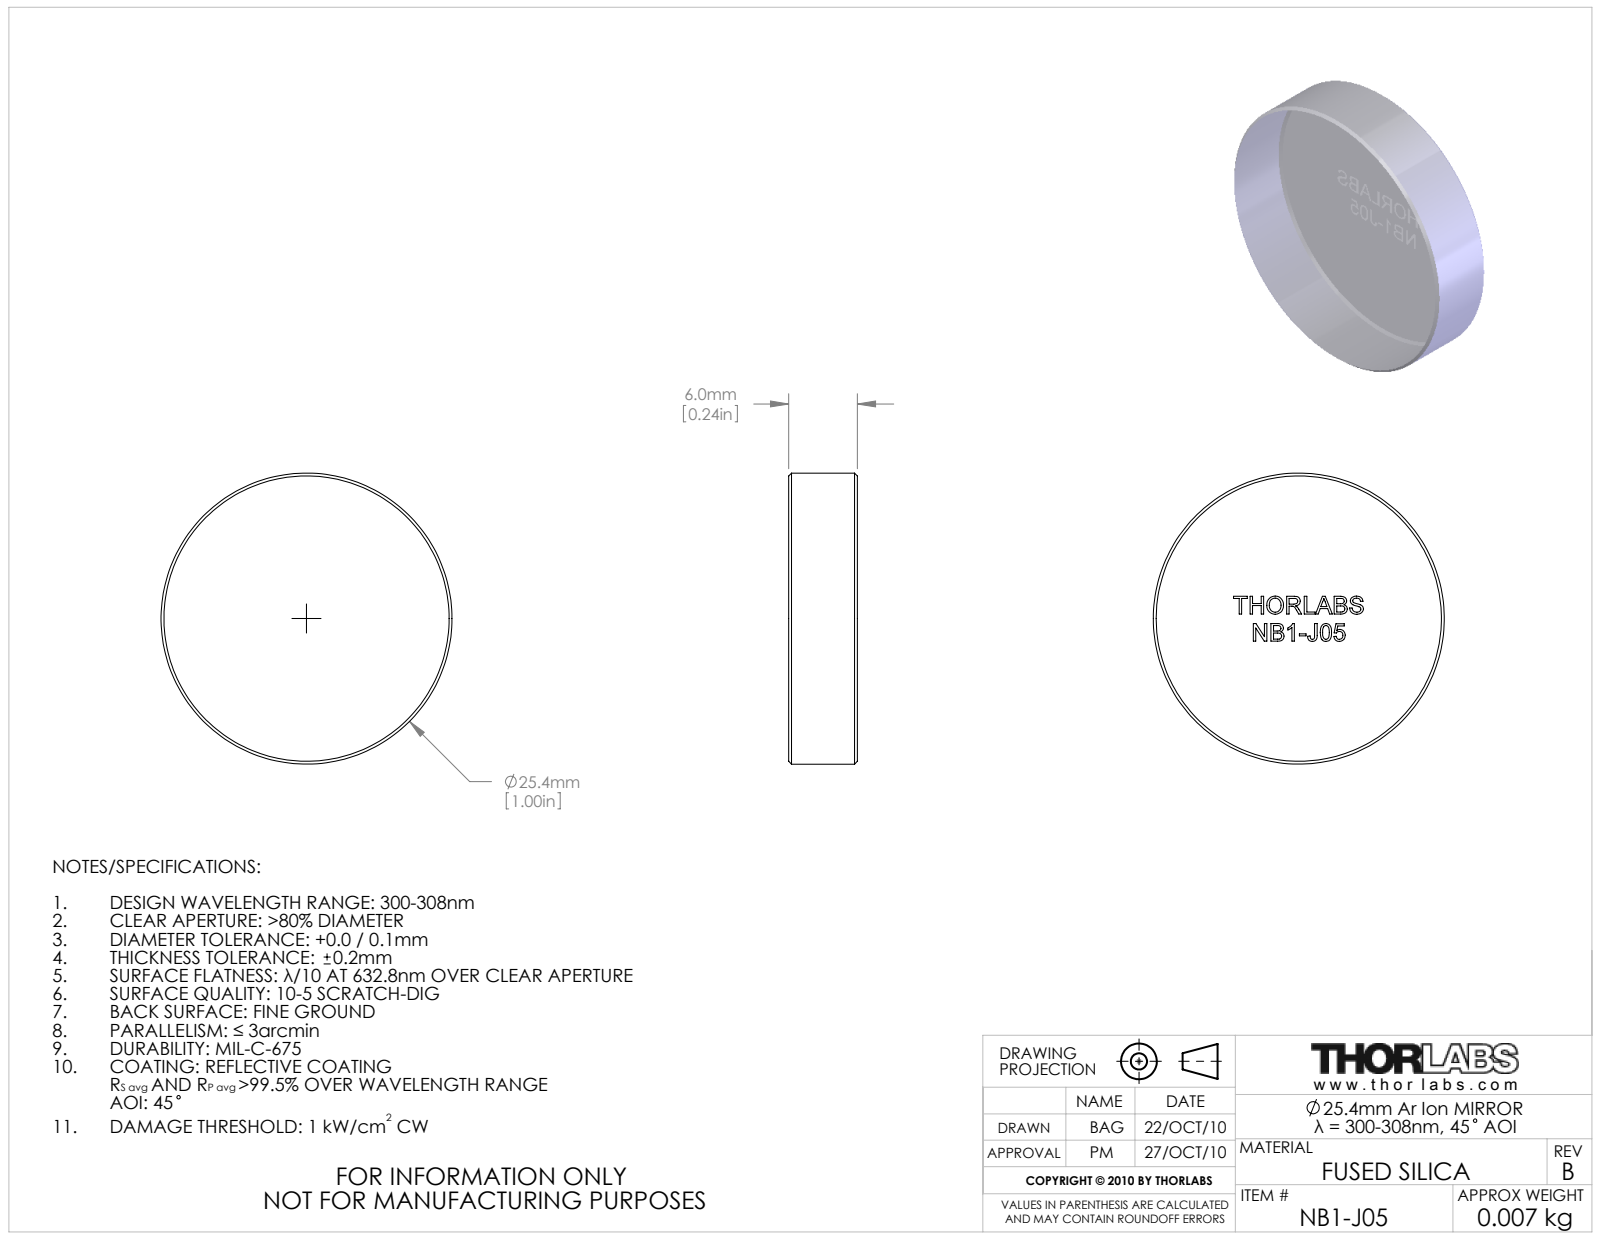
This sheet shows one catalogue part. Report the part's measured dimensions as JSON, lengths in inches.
{"part_name": "8775-E0W", "step_written_by": "SolidWorks 2009 (AUTOMOTIVE_DESIGN)", "units": "inches", "bodies": {"solids": 1, "faces": 206, "planar": 123, "cylindrical": 2, "other": 81}, "overall_size": [1, 1, 0.236], "volume_in3": 0.185, "surface_area_in2": 2.276, "round_bosses_or_shafts": [[1, 1]], "face_to_face_distances": [0.236, 0.061, 0.094, 0.076, 0.115, 0.163, 0.038, 0.175, 0.035, 0.093]}
